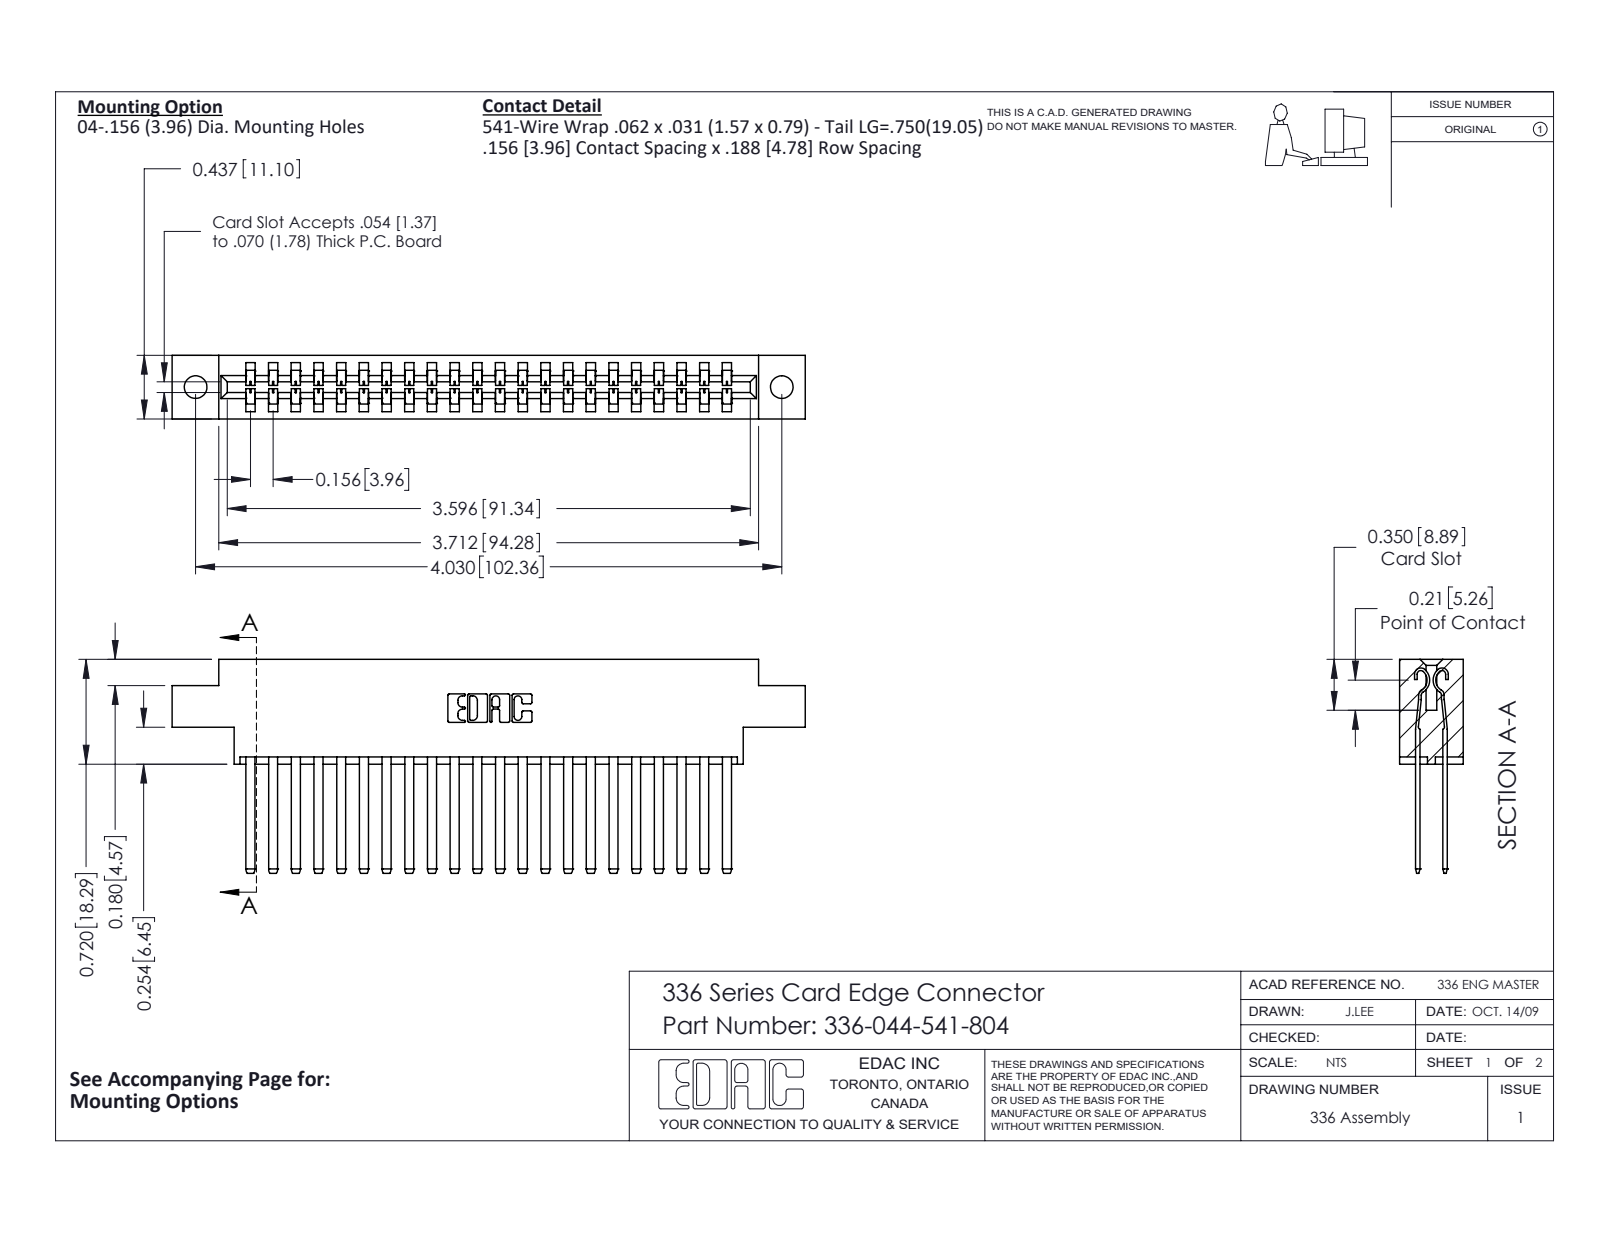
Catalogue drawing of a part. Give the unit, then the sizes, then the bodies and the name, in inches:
Units: inches
Overall size (bounding box): 4.353 × 1.47 × 0.437
Round holes (diameter × count): ⌀0.156 ×2
Partial cylindrical surfaces — rounded edges, fillets, slot ends (radius × count): R0.004 ×88, R0.056 ×44, R0.01 ×22, R0.007 ×6, R0.031 ×6, R0.022 ×4, R0.04 ×4, R0.026 ×3
Main face-to-face distances: 0.188, 0.328, 0.14, 0.297, 0.109, 0.031, 0.437, 0.033, 0.156, 0.181
Hole centre spacings: 4.03
Volume: 0.997 in³ · Surface area: 31.58 in²
Bodies: 45 solids, 1966 faces (1218 planar, 748 cylindrical, 0 other)
Part name (STEP PRODUCT): 336 Part_Offset - .156 Dia - TH; 336-290-001_336-290-541; 336-044-541-804
STEP written by: SolidWorks 2020 (CONFIG_CONTROL_DESIGN)
